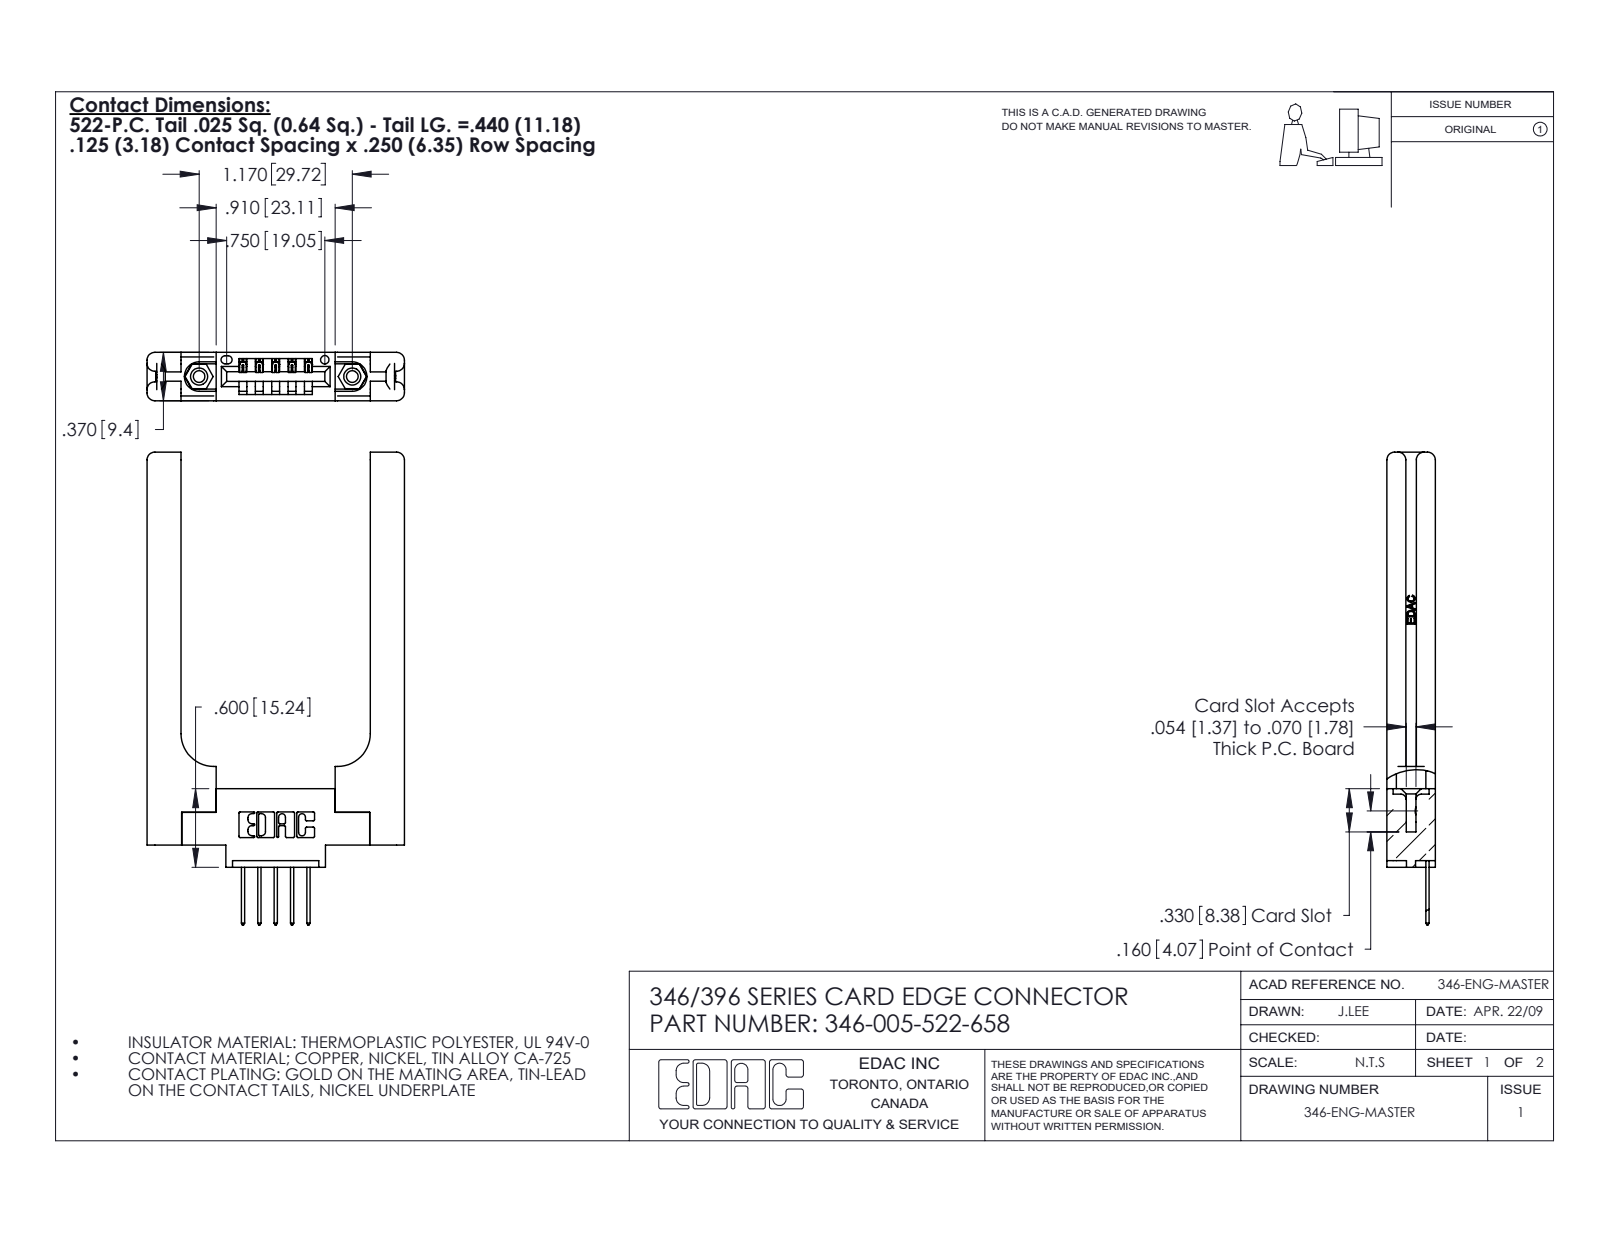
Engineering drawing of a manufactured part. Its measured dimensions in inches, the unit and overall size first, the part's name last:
Units: inches
Overall size (bounding box): 3.61 × 1.966 × 0.37
Round holes (diameter × count): ⌀0.089 ×2, ⌀0.125 ×2, ⌀0.156 ×2, ⌀0.064 ×1
Round bosses / shafts (diameter × count): ⌀0.155 ×2
Partial cylindrical surfaces — rounded edges, fillets, slot ends (radius × count): R0.01 ×22, R0.06 ×16, R0.006 ×10, R0.01 ×10, R0.007 ×6, R0.031 ×6, R0.026 ×3, R0.03 ×2
Main face-to-face distances: 0.37, 0.15, 0.22, 0.072, 1.446, 0.148, 0.25, 0.075, 0.071, 0.26
Hole centre spacings: 0.246, 0.969, 1.17
Volume: 0.724 in³ · Surface area: 16.15 in²
Bodies: 10 solids, 686 faces (442 planar, 184 cylindrical, 60 other)
Part name (STEP PRODUCT): 346-005-522-658; 346-220-058_345-220-058; 346 Part_0.170 Offset - 0.156 Dia-TH; 345-250-001_345-250-001-102 (+1 more)
STEP written by: SolidWorks 2020 (CONFIG_CONTROL_DESIGN)
